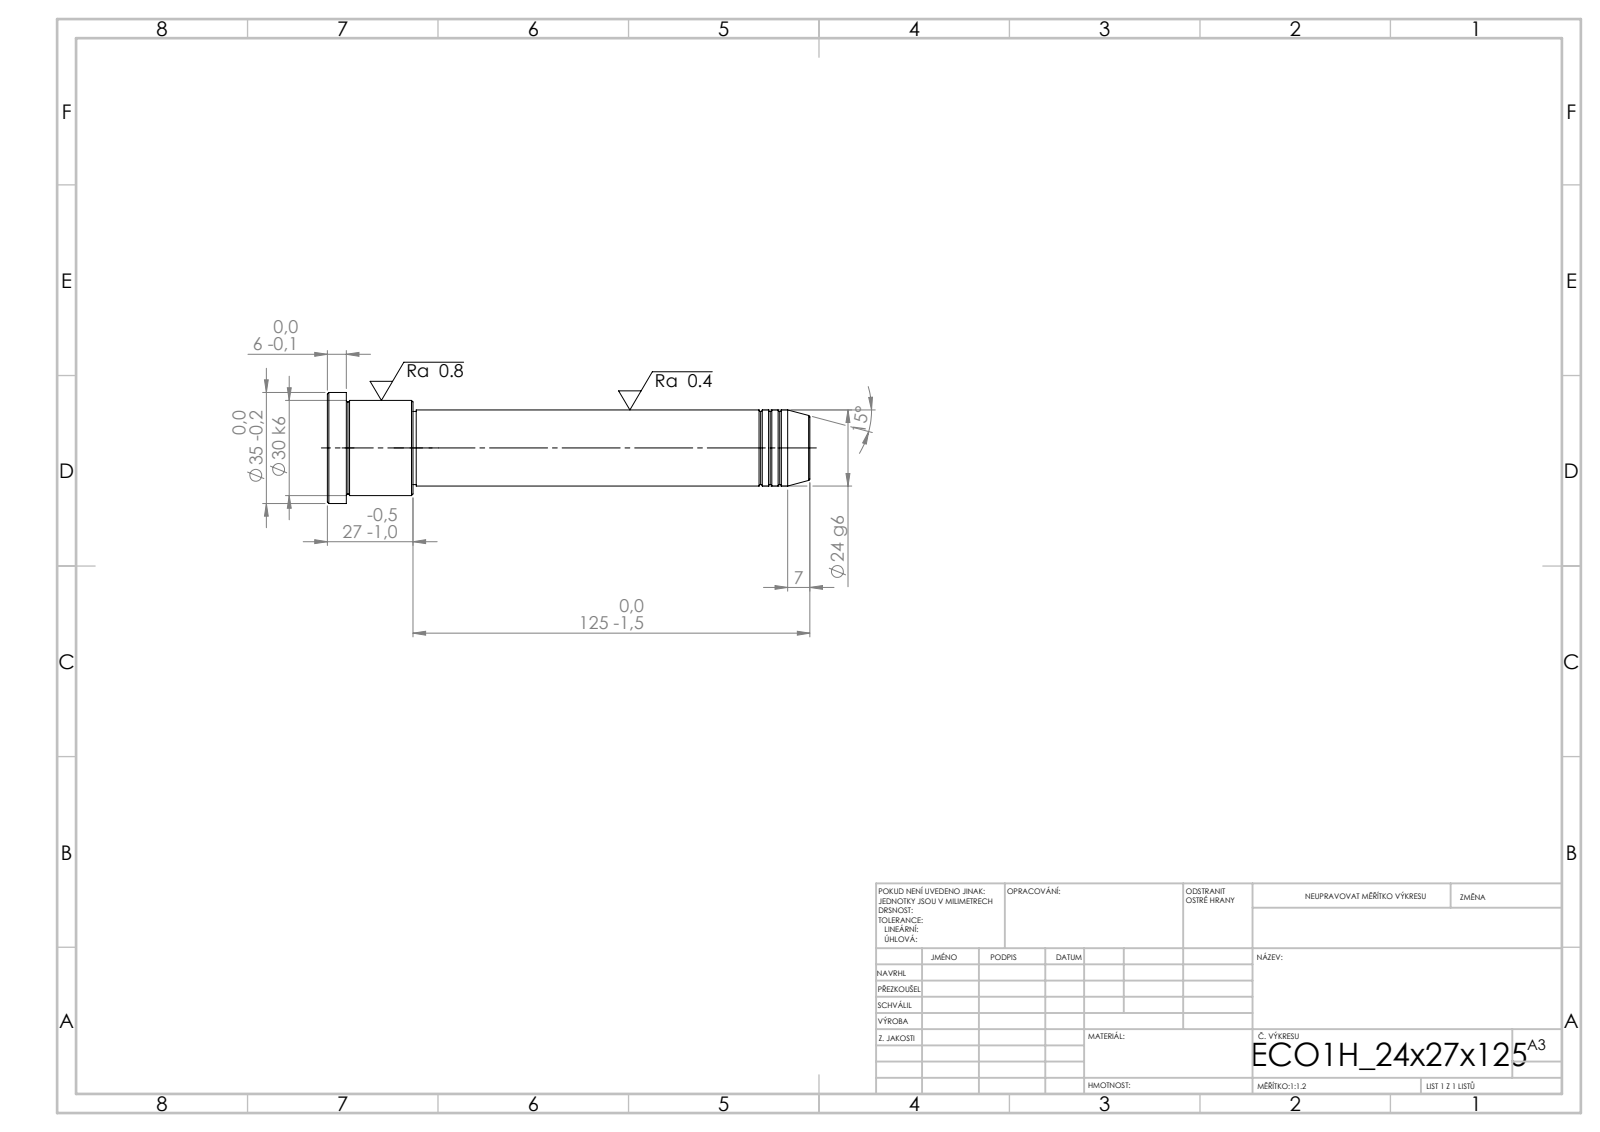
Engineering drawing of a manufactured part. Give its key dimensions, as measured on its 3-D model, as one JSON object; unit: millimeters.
{"step_written_by": "SolidWorks 2019 (CONFIG_CONTROL_DESIGN)", "units": "millimeters", "bodies": {"solids": 1, "faces": 43, "planar": 5, "cylindrical": 14, "other": 24}, "overall_size": [152, 35, 35], "volume_mm3": 76508, "surface_area_mm2": 14007, "round_bosses_or_shafts": [[35, 1], [30, 1], [24, 1], [23, 1]], "face_to_face_distances": [152, 146, 6, 125, 21, 27, 124, 1, 22, 28]}
